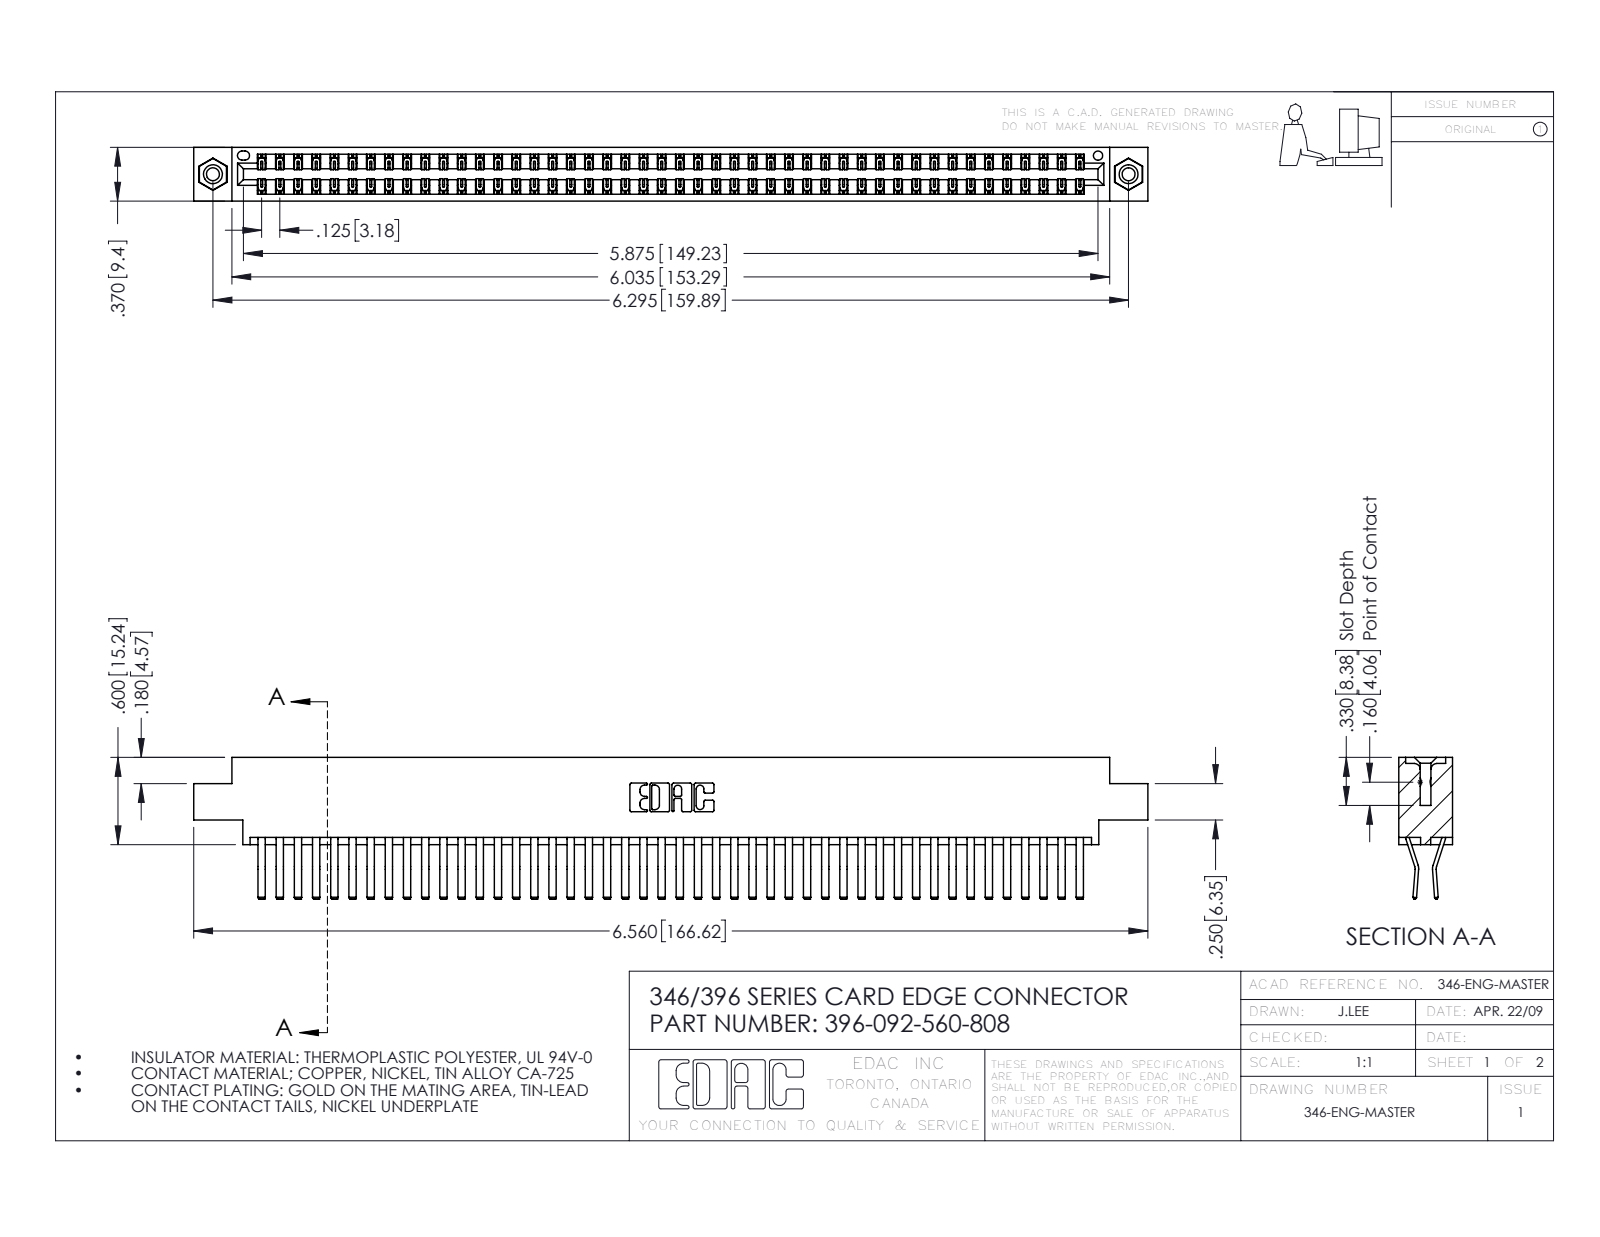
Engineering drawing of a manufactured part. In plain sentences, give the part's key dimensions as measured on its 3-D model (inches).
The part is named "396-092-560-808; 345-292-001_560 Tail; 346 Part_0.170 Offset - 0.156 Dia-TI; 345-250-001_345-250-003-102". Its 3-D file was written by "SolidWorks 2016 (CONFIG_CONTROL_DESIGN)". It is 95 solids with 5154 faces: 3332 planar, 1806 cylindrical and 16 other. Overall it measures 6.56 by 0.975 by 0.37 inches. Its volume is 1.02 cubic inches and its surface area 38.53 square inches. Round holes: 2 of diameter 0.089, 2 of diameter 0.125, 2 of diameter 0.156, 1 of diameter 0.064. Round bosses or shafts: 2 of diameter 0.155. Partial cylindrical surfaces (rounded edges, fillets, slot ends): 138 of radius 0.006, 22 of radius 0.01, 6 of radius 0.007, 6 of radius 0.031, 3 of radius 0.026, 2 of radius 0.01, 2 of radius 0.014, 2 of radius 0.022. The main face-to-face distances are 0.048, 0.322, 0.37, 0.025, 0.25, 0.072, 0.298, 0.275, 0.222, 0.148. The hole center spacings are 0.246, 6.086, 6.295.
